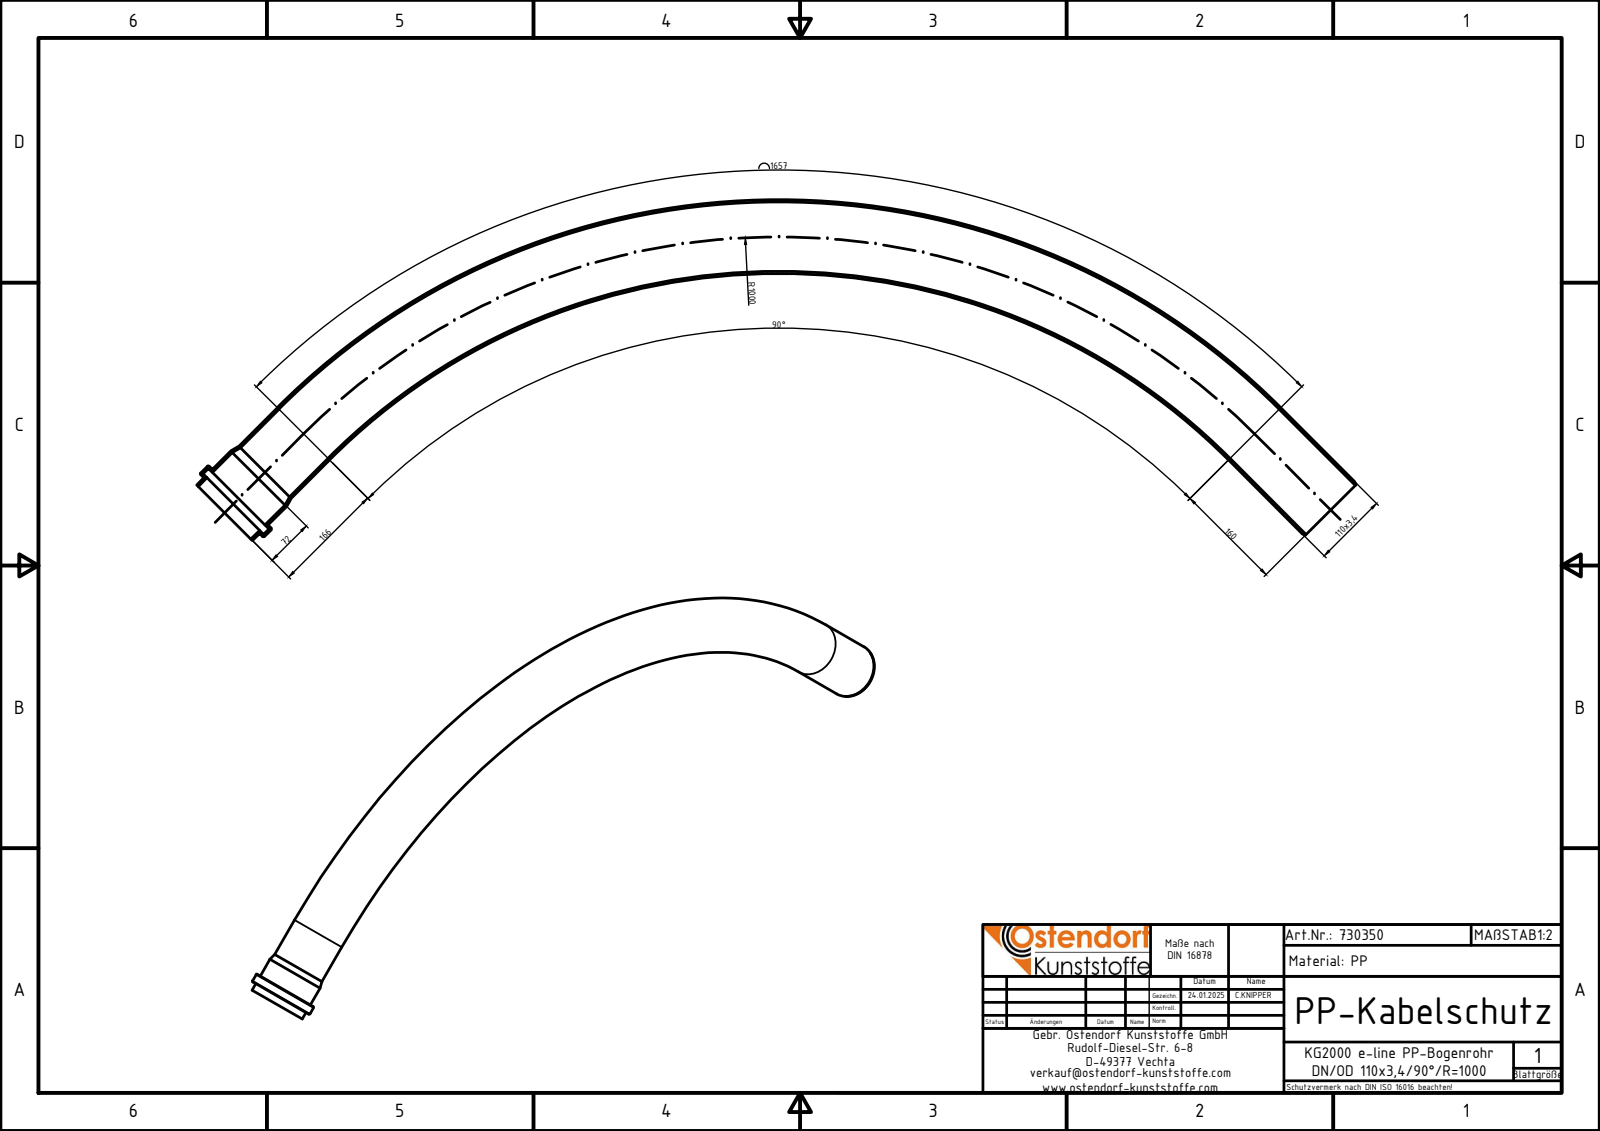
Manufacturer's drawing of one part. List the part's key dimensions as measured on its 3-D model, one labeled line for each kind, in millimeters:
Part name (STEP PRODUCT): 730350z
STEP written by: Autodesk Inventor 2024 (AUTOMOTIVE_DESIGN)
Units: millimetres
Bodies: 1 solid, 23 faces (6 planar, 10 cylindrical, 7 other)
Overall size (bounding box): 862.05 × 253.35 × 67
Volume: 273 630 mm³ · Surface area: 322 495 mm²
Round holes (diameter × count): ⌀51.6 ×2, ⌀55.2 ×1, ⌀63.6 ×1
Round bosses / shafts (diameter × count): ⌀55 ×2, ⌀67 ×1, ⌀58.6 ×1
Main face-to-face distances: 1.7, 7.3, 5.6, 9, 7.5, 9.2, 14.8, 16.5
